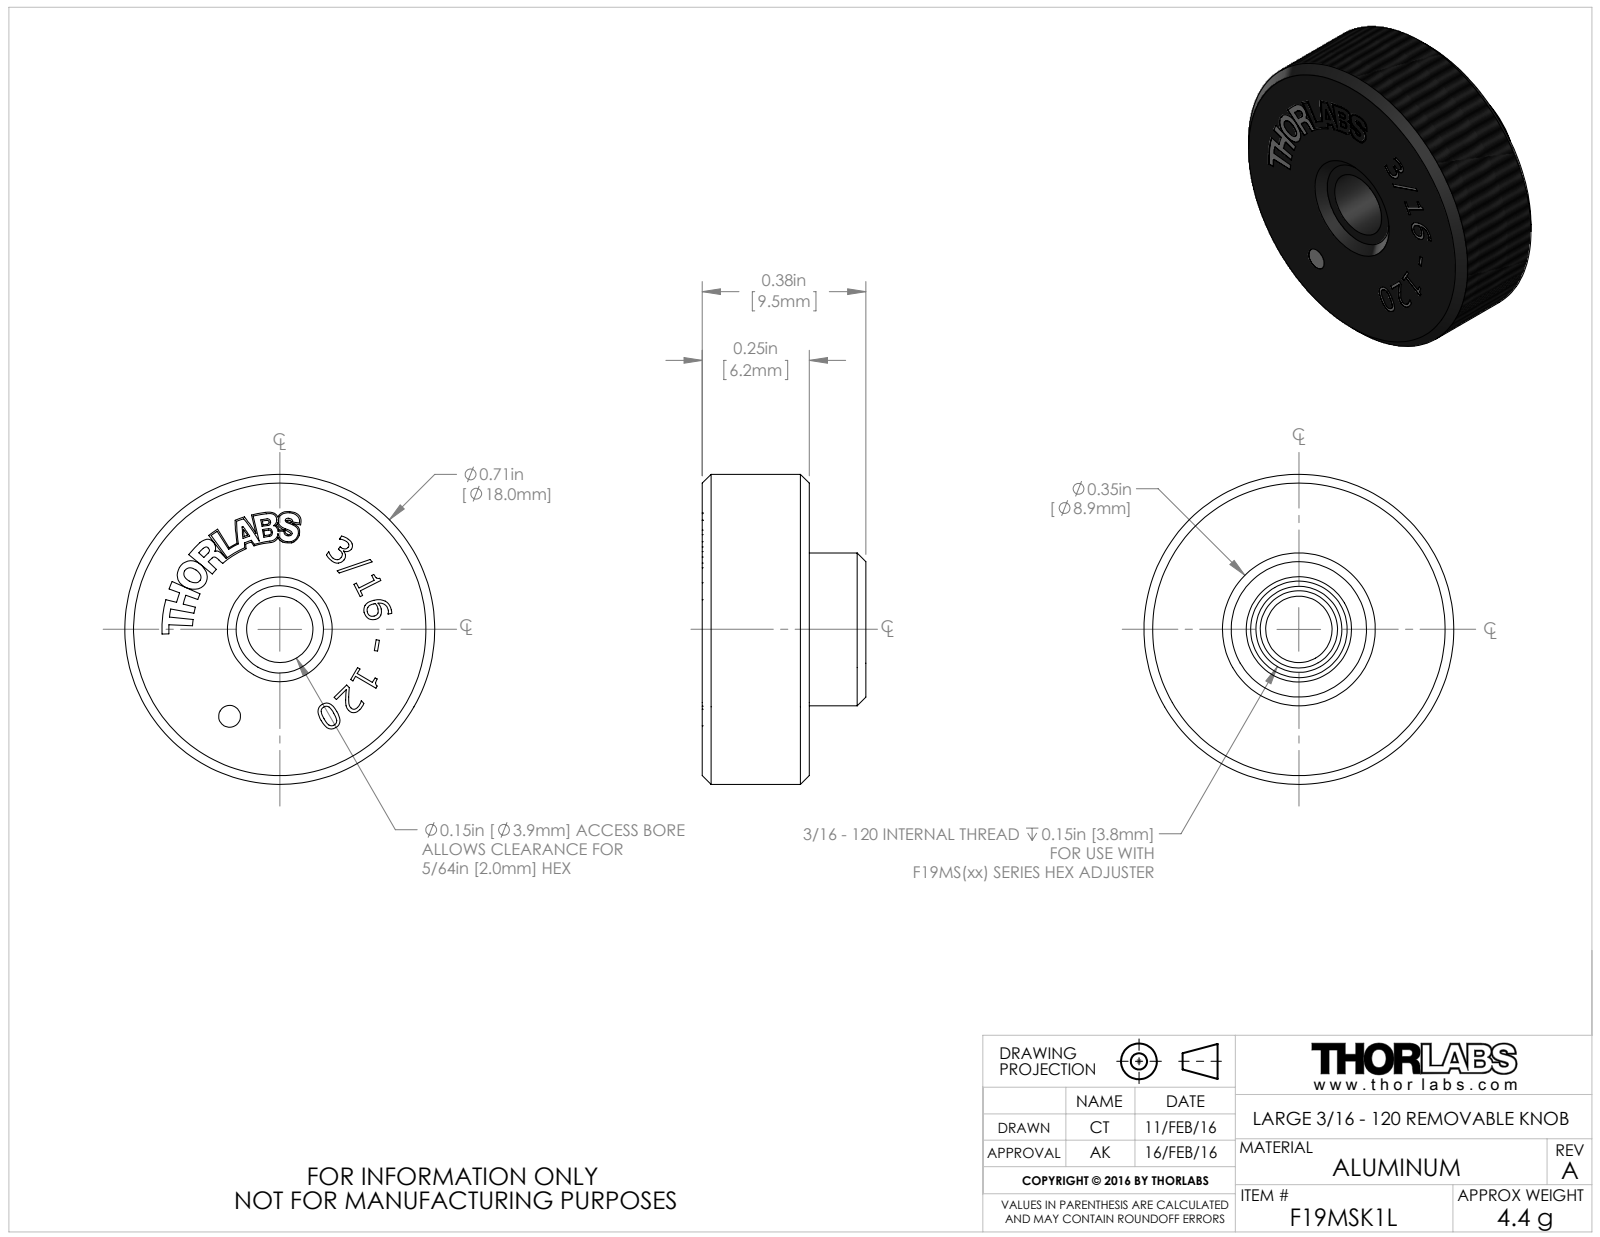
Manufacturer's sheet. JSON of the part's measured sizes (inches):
{"part_name": "TTN093552-E0W", "step_written_by": "SolidWorks 2014 (CONFIG_CONTROL_DESIGN)", "units": "inches", "bodies": {"solids": 1, "faces": 309, "planar": 106, "cylindrical": 14, "other": 189}, "overall_size": [0.71, 0.71, 0.375], "volume_in3": 0.098, "surface_area_in2": 1.604, "round_holes": [[0.05, 1], [0.152, 1], [0.177, 1], [0.217, 1], [0.221, 1]], "round_bosses_or_shafts": [[0.71, 1], [0.35, 1]], "face_to_face_distances": [0.245, 0.375, 0.13, 0.05, 0.02, 0.225, 0.195, 0.18, 0.175, 0.355], "hole_center_spacings": [0.23]}
